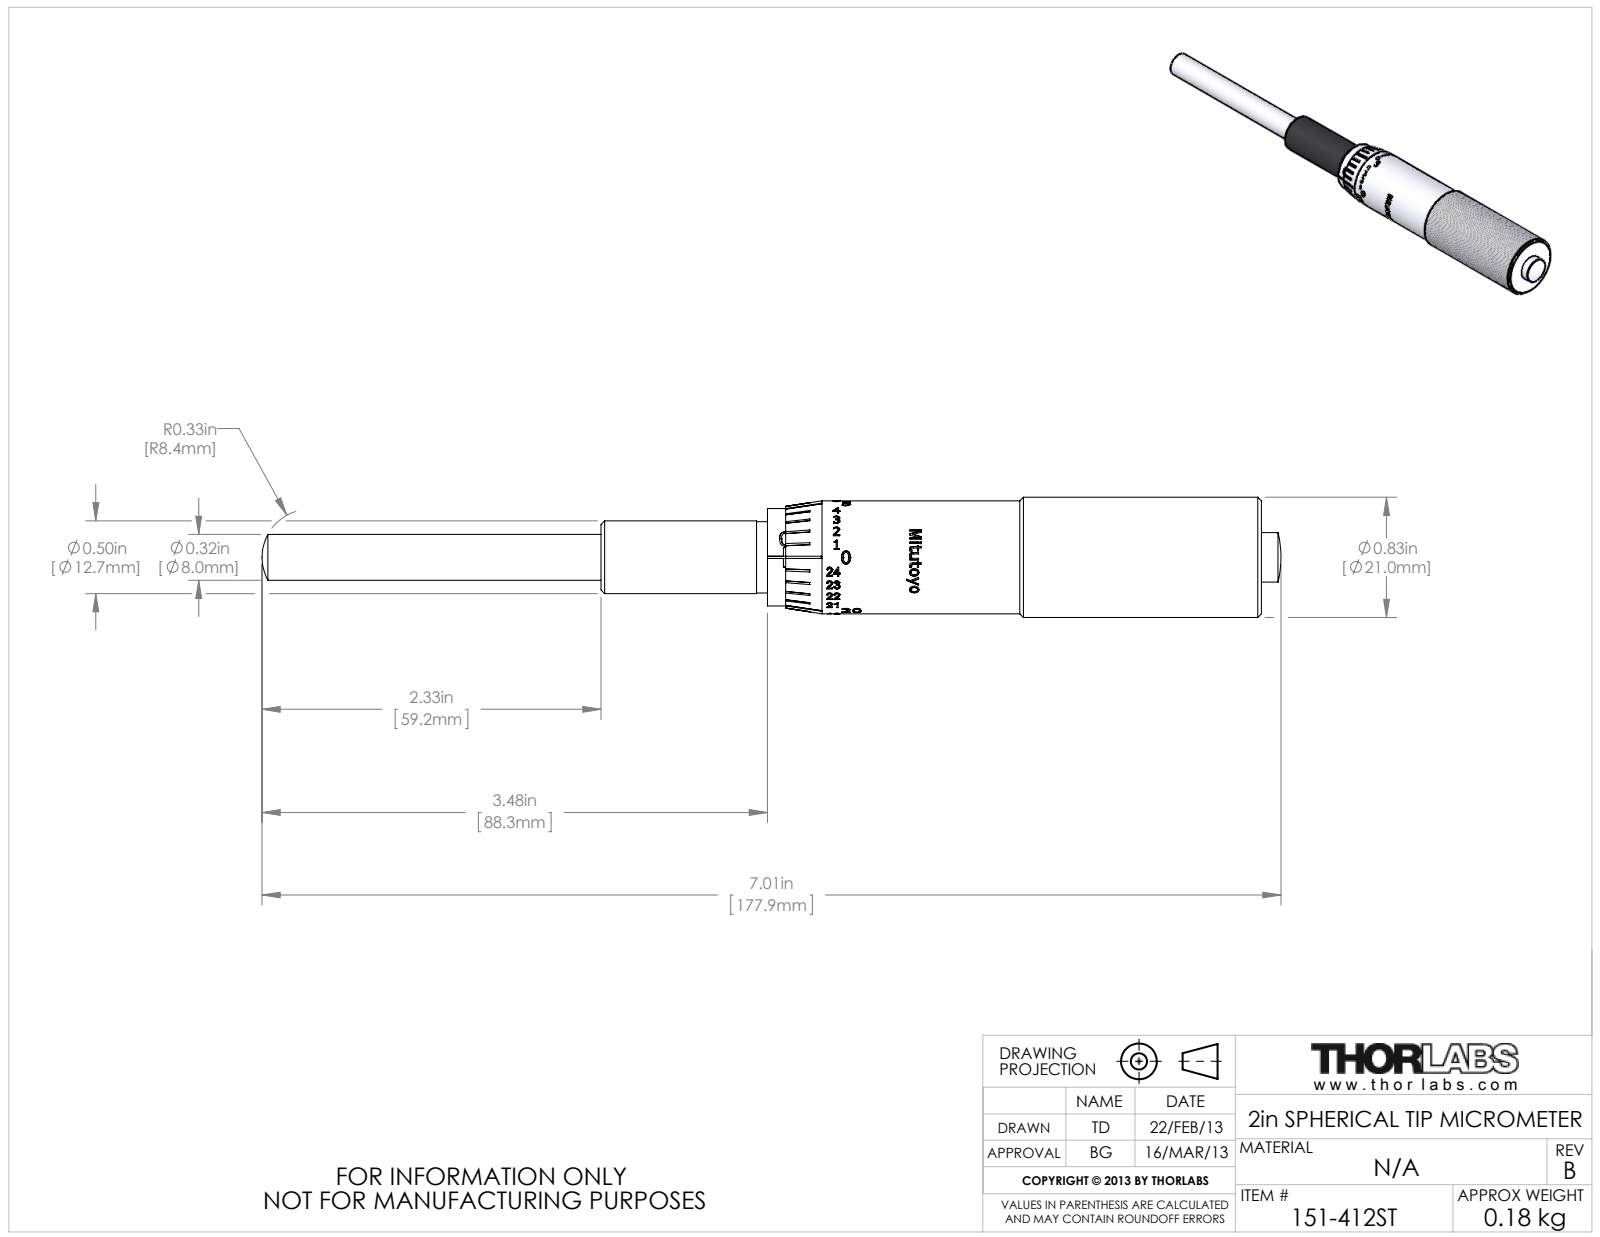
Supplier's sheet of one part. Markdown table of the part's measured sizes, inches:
| quantity | value |
| --- | --- |
| part name | 13434-E0W |
| STEP written by | SolidWorks 2012 (AUTOMOTIVE_DESIGN) |
| units | inches |
| bodies | 2 solids, 1710 faces (948 planar, 136 cylindrical, 626 other) |
| overall size | 7.005 × 0.827 × 0.827 |
| volume | 2.279 in³ |
| surface area | 28.42 in² |
| round holes (diameter × count) | 0.316 × 1, 0.345 × 1, 0.37 × 1, 0.68 × 1 |
| round bosses / shafts (diameter × count) | 0.827 × 1, 0.777 × 1, 0.67 × 1, 0.5 × 1, 0.49 × 1, 0.43 × 1, 0.34 × 1, 0.315 × 1 |
| partial cylindrical surfaces (radius × count) | 0.334 × 1, 0.388 × 1 |
| main face-to-face distances | 2.065, 1.185, 0.88, 2.21, 3.395, 1.33, 4.54, 3.355, 2.475, 1.145 |
